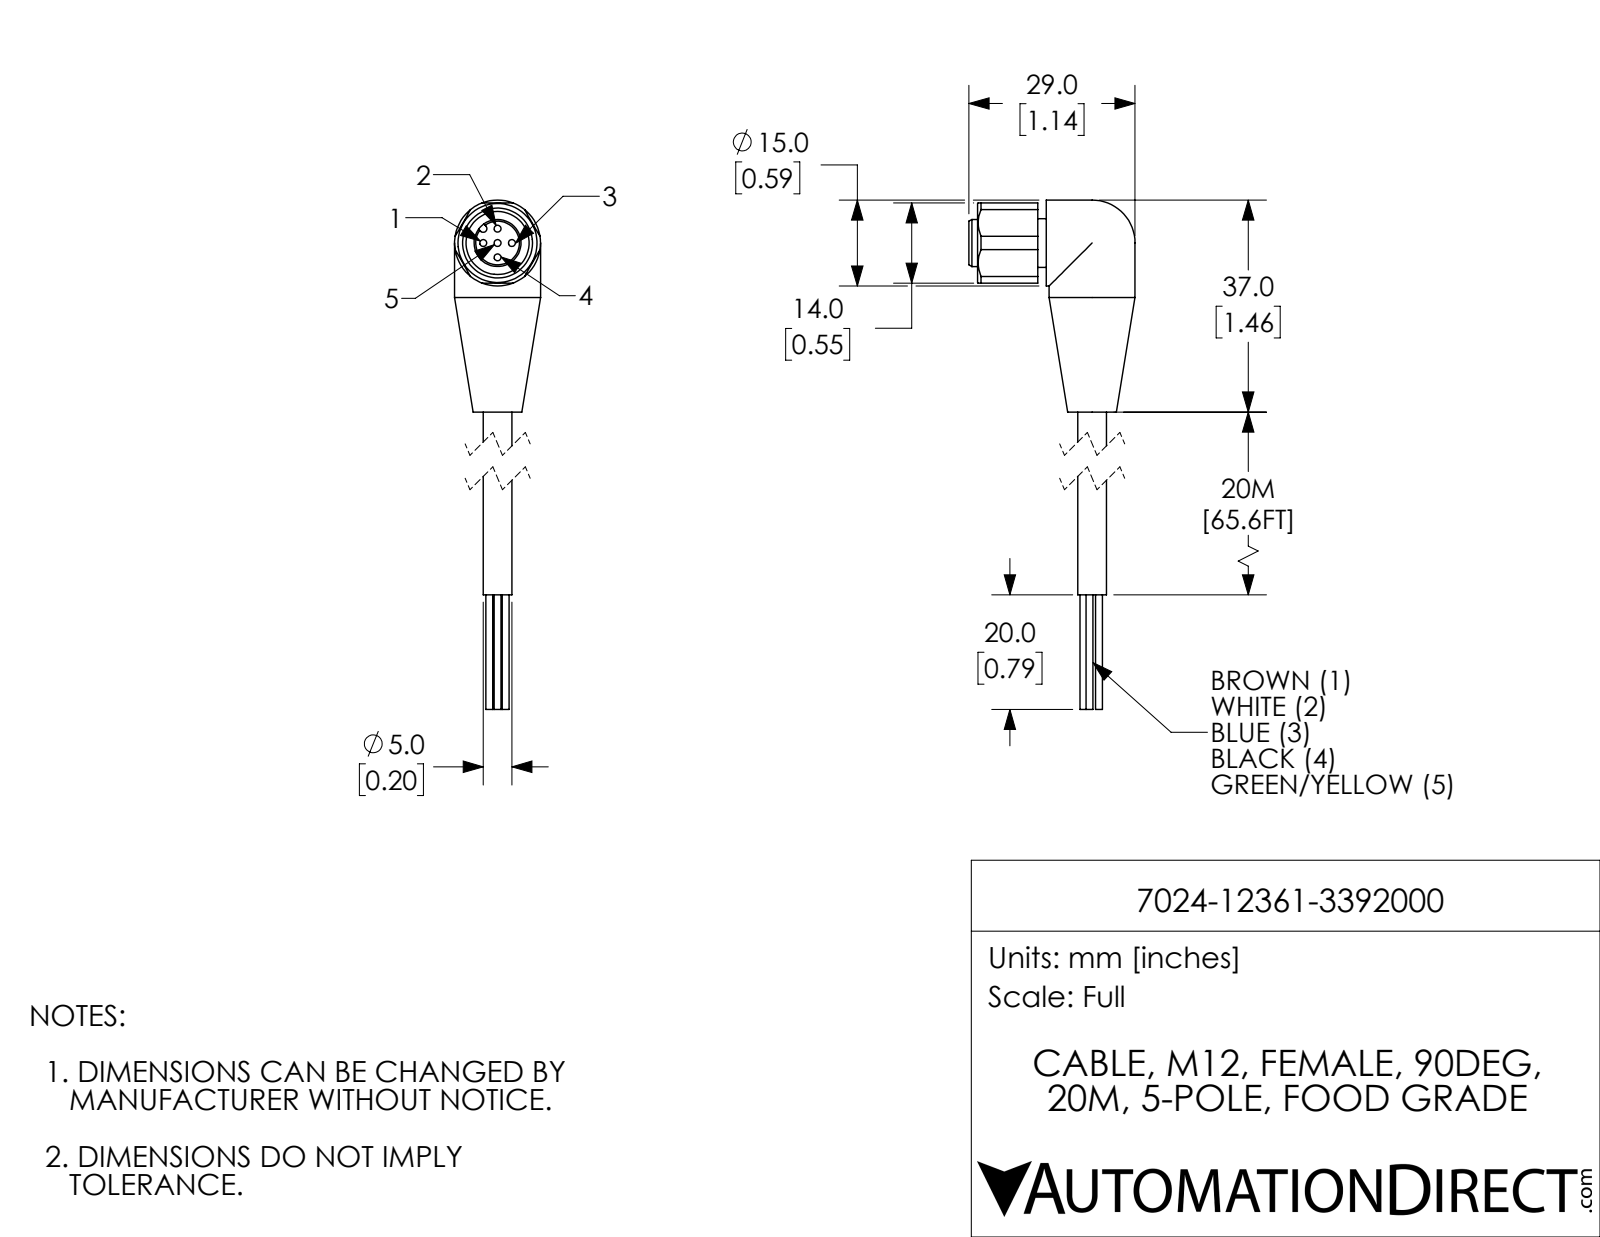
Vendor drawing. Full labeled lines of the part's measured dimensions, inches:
Part name (STEP PRODUCT): 7024-12361-3392000
STEP written by: SolidWorks 2018 (AUTOMOTIVE_DESIGN)
Units: inches
Bodies: 1 solid, 76 faces (26 planar, 40 cylindrical, 10 other)
Overall size (bounding box): 3.425 × 1.142 × 0.591
Volume: 0.453 in³ · Surface area: 6.14 in²
Round holes (diameter × count): ⌀0.047 ×5, ⌀0.433 ×1
Round bosses / shafts (diameter × count): ⌀0.047 ×5, ⌀0.591 ×2, ⌀0.335 ×1, ⌀0.323 ×1, ⌀0.197 ×1
Partial cylindrical surfaces — rounded edges, fillets, slot ends (radius × count): R0.026 ×1
Main face-to-face distances: 0.551, 0.059, 0.472, 0.177, 0.118, 0.531, 0.354, 0.886, 1.437, 0.413
Hole centre spacings: 0.098, 0.139, 0.197
